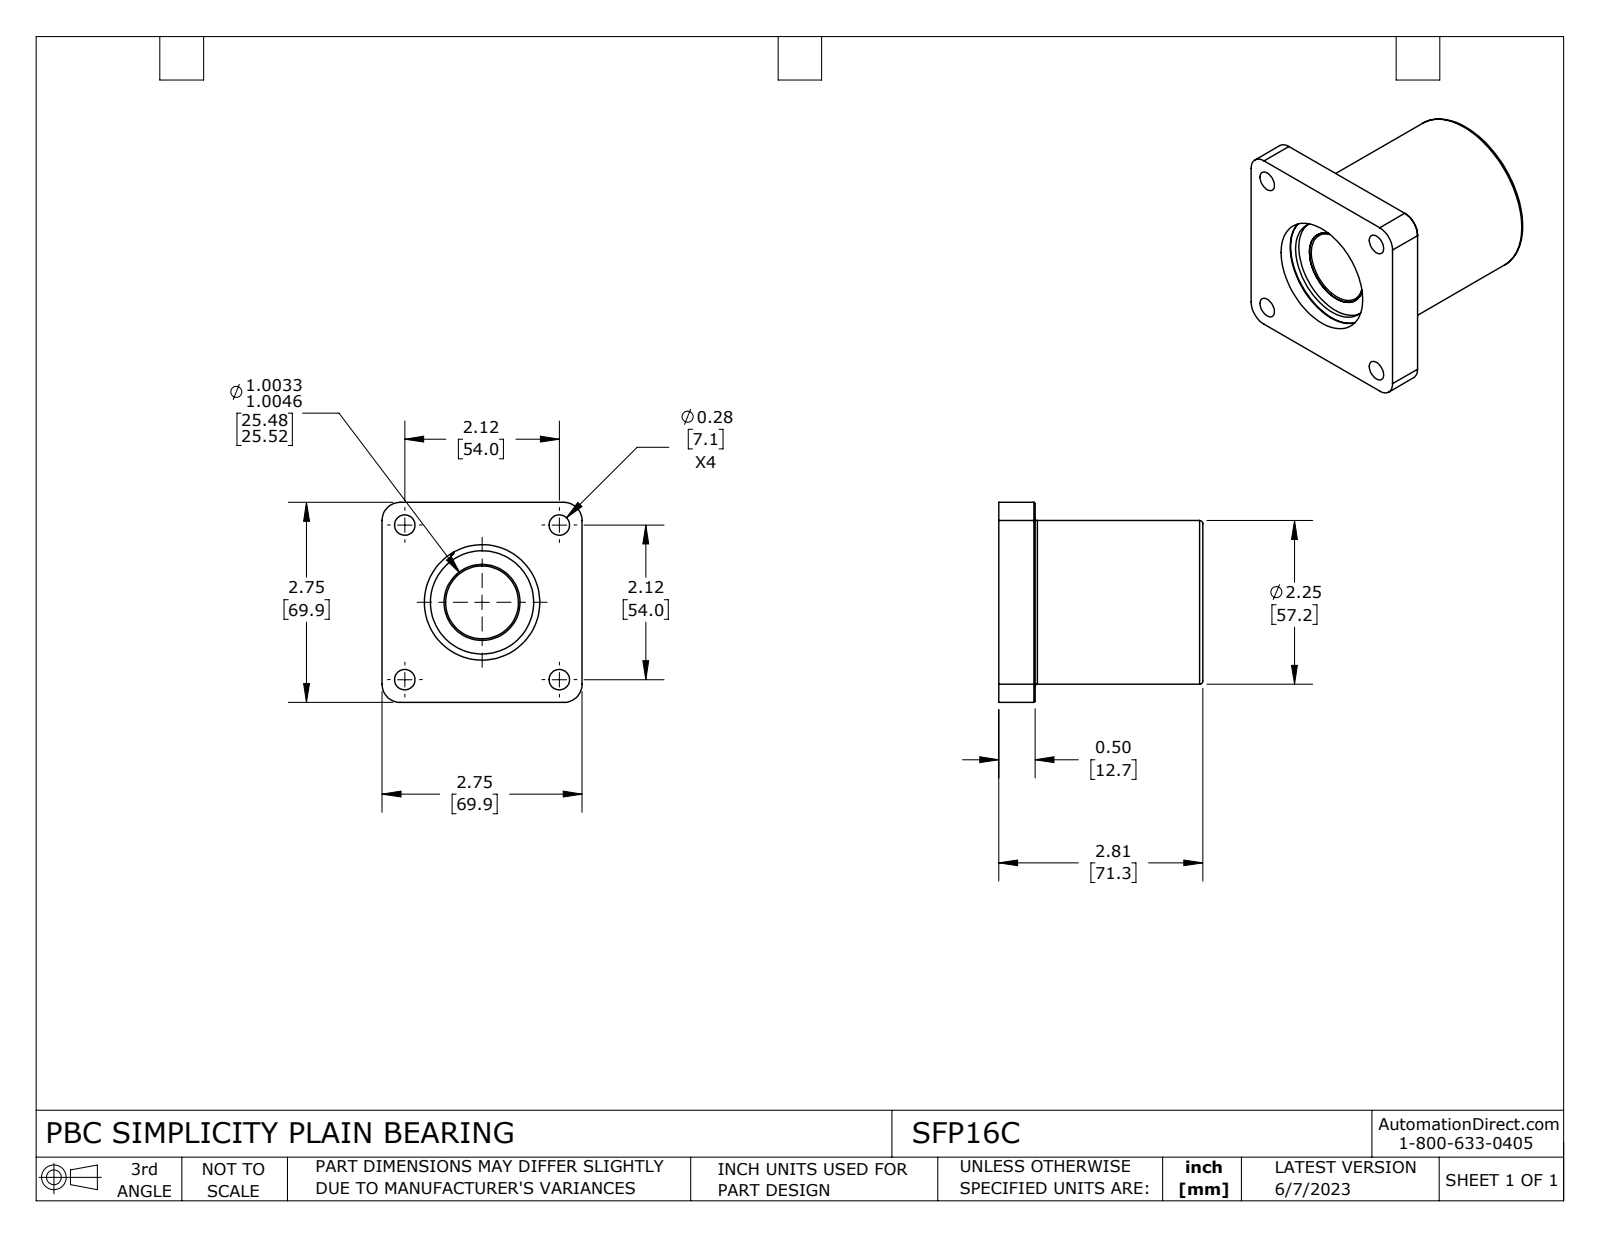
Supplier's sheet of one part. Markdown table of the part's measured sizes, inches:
| quantity | value |
| --- | --- |
| part name | SFP16C |
| STEP written by | SolidWorks 2021 (CONFIG_CONTROL_DESIGN) |
| units | inches |
| bodies | 7 solids, 169 faces (41 planar, 74 cylindrical, 54 other) |
| overall size | 2.807 × 2.75 × 2.75 |
| volume | 9.813 in³ |
| surface area | 91.86 in² |
| round holes (diameter × count) | 0.281 × 4, 1.001 × 1, 1.045 × 1, 1.419 × 1, 1.587 × 1, 1.658 × 1 |
| round bosses / shafts (diameter × count) | 2.25 × 1, 1.675 × 1, 1.562 × 1, 1.471 × 1, 1.399 × 1 |
| partial cylindrical surfaces (radius × count) | 0.021 × 4, 0.25 × 4, 0.016 × 2, 0.026 × 2 |
| main face-to-face distances | 0.5, 2.75, 2.807, 2.307, 0.2, 2.607, 2.524, 2.024, 0.283, 0.282 |
| hole center spacings | 1.503, 2.125, 3.006 |
